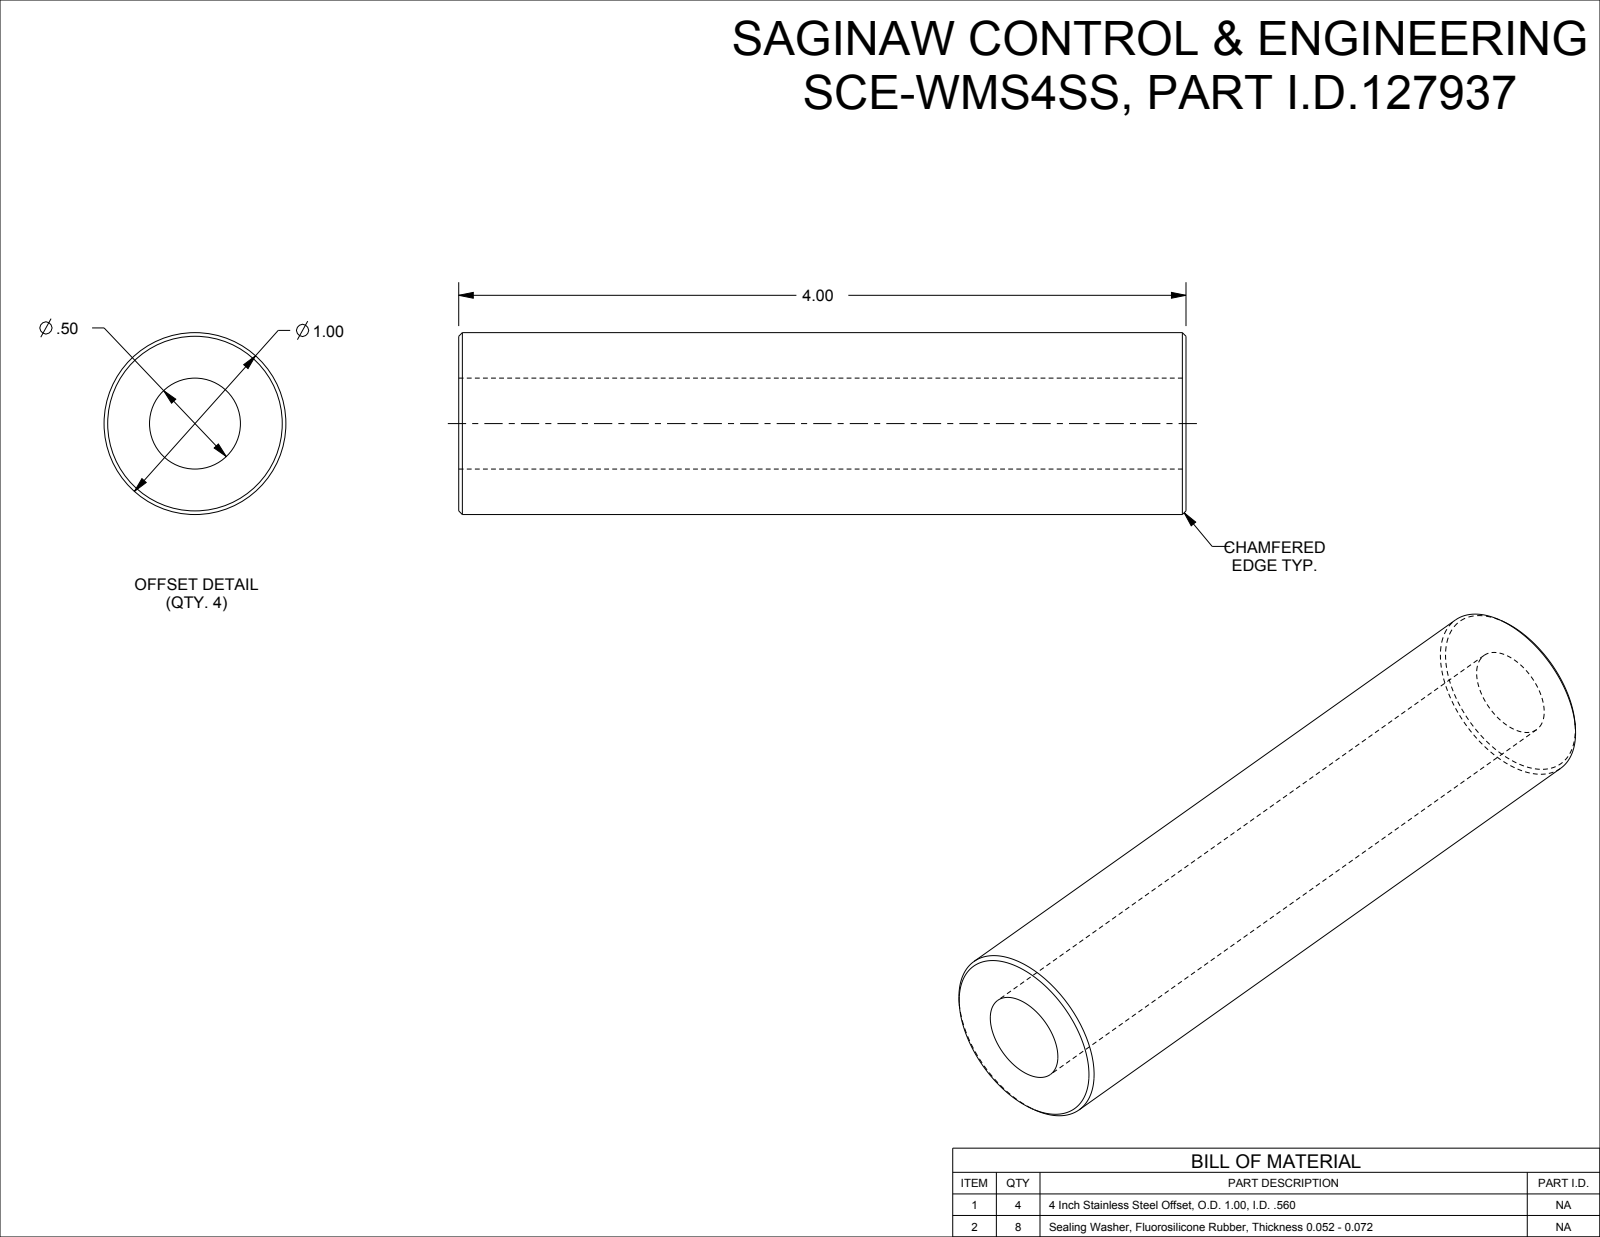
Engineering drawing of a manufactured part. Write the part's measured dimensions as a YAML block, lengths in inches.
part_name: "SCE-WMS4SS"
step_written_by: "SolidWorks 2019 (CONFIG_CONTROL_DESIGN)"
units: inches
bodies: {solids: 3, faces: 14, planar: 6, cylindrical: 6, other: 2}
overall_size: [4.124, 1, 1]
volume: 2.407
surface_area: 22.08
round_holes:
  - {diameter: 0.355, count: 1}
  - {diameter: 0.5, count: 1}
round_bosses_or_shafts:
  - {diameter: 1, count: 1}
  - {diameter: 0.812, count: 1}
face_to_face_distances: [4, 0.062, 4.062, 4.124]
